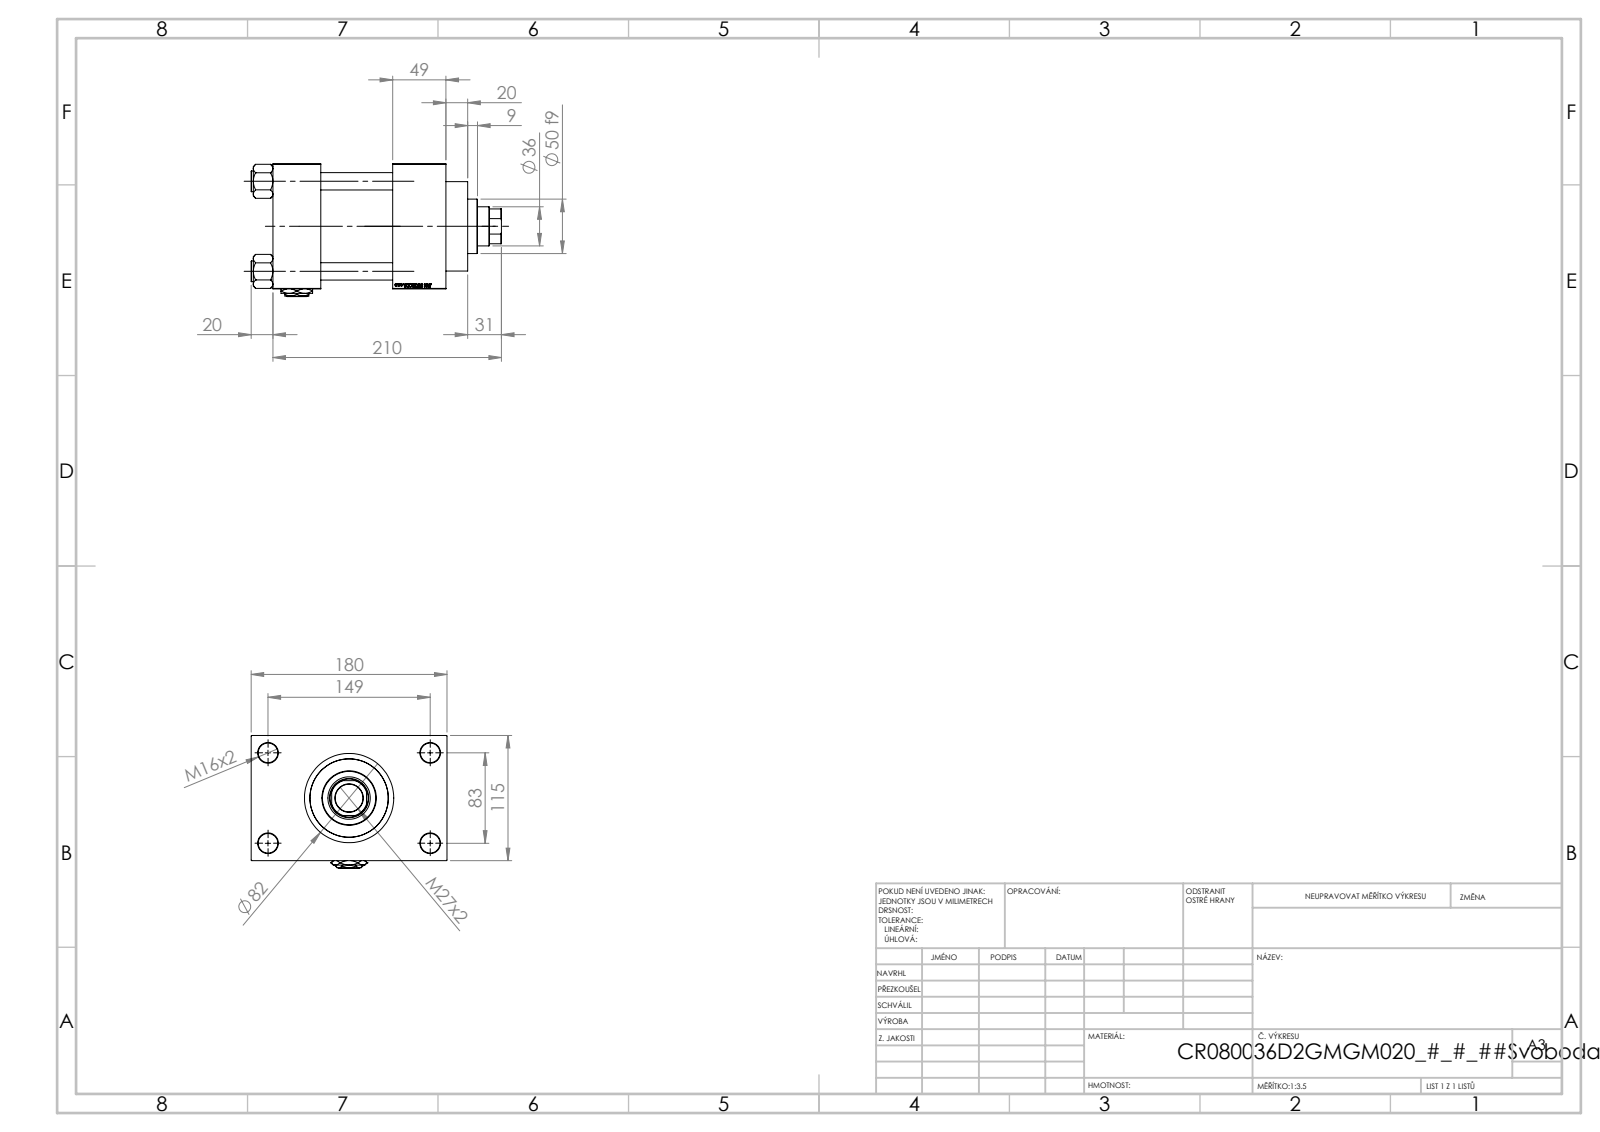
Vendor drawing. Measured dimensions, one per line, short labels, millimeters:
name: V215CR_D_Body; V215CR_D_TYCINKA; Zatka_pro_OIL_PORT; NUT_M5_D (+2 more)
written by: SolidWorks 2019 (CONFIG_CONTROL_DESIGN)
unit: mm
bodies: 12 solids, 1204 faces (569 planar, 95 cylindrical, 540 other)
size: 230 × 180 × 122
volume: 1 976 000 mm³; area: 300 233 mm²
holes: 4× ⌀16, 4× ⌀18, 3× ⌀7, 3× ⌀26.44, 3× ⌀35, 1× ⌀25.5, 1× ⌀36, 1× ⌀39, 1× ⌀61, 1× ⌀72, 1× ⌀80
bosses: 4× ⌀19, 1× ⌀86, 1× ⌀82, 1× ⌀50
rounds: 1× R17.5
face distances: 115, 66, 110, 49, 44, 159, 32.5, 147.5, 20, 69
hole spacings: 33.15, 58.48, 82.7, 85.28, 89.24, 115.85, 142.43, 83
